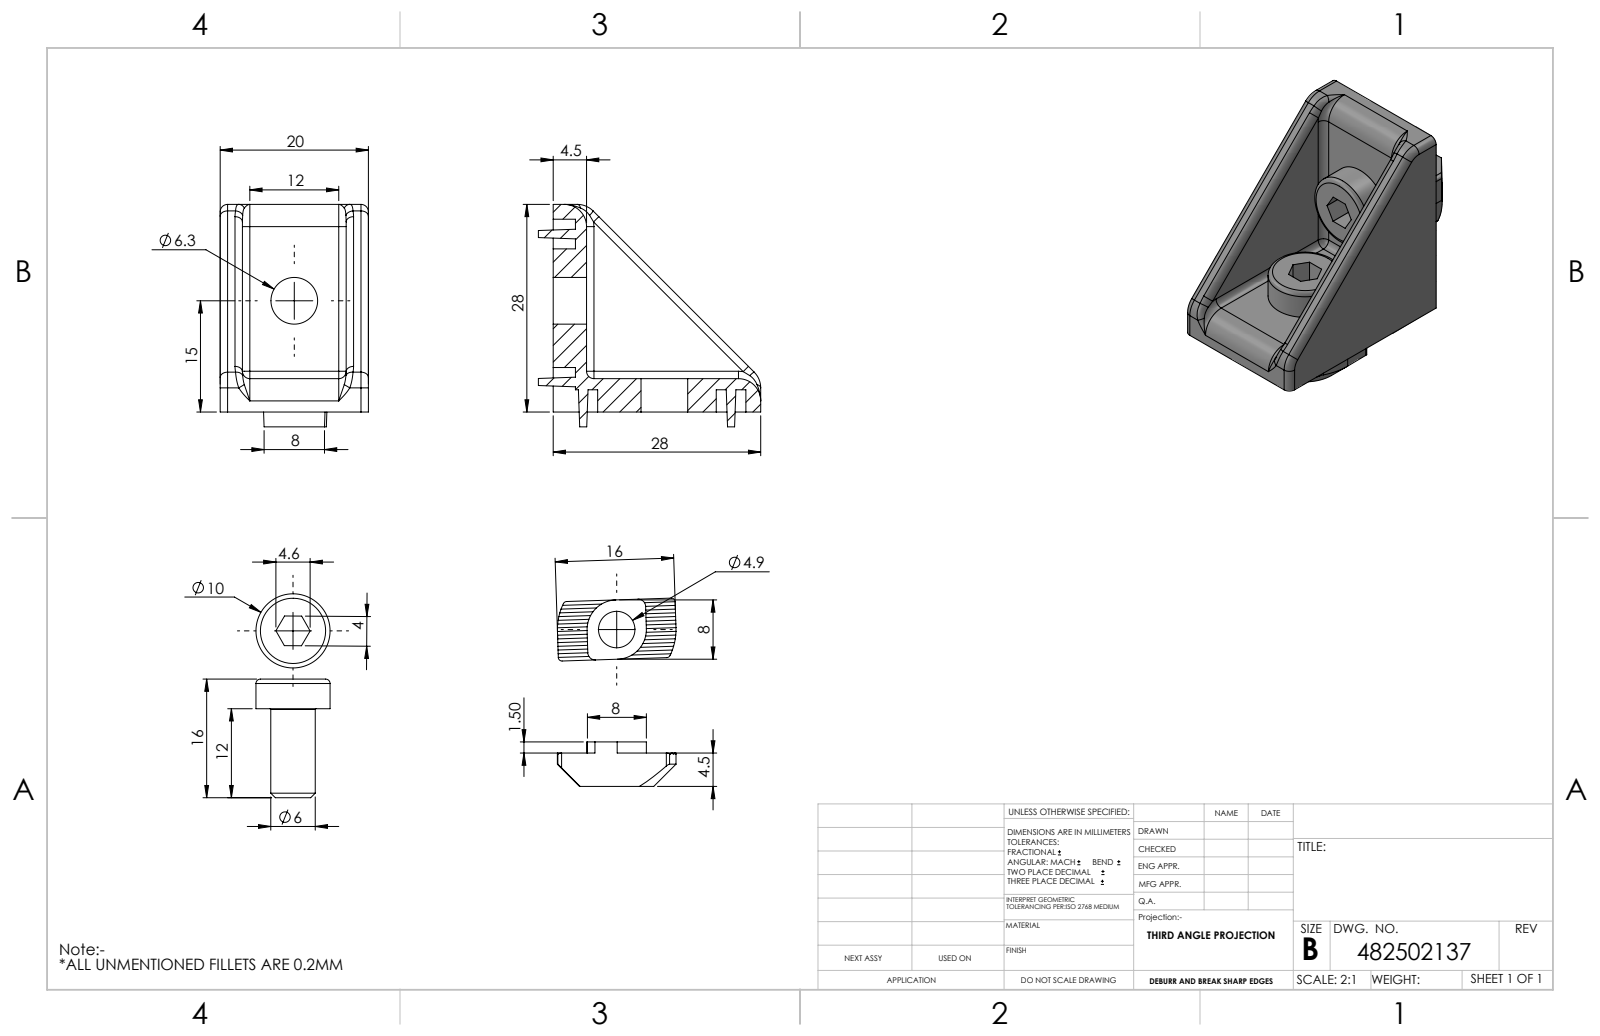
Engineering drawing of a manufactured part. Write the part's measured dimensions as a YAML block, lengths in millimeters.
part_name: "482502137 Winkel 20x28 inkl Bef; Syskomp 482501587 Winkel 20x28; DIN 7984 M6 x 12; Syskomp 482501753 Hammermutter N8 M6 verzinkt"
step_written_by: "Autodesk Inventor 2012 (AUTOMOTIVE_DESIGN)"
units: millimeters
bodies: {solids: 5, faces: 231, planar: 150, cylindrical: 47, other: 34}
overall_size: [35.5, 35.5, 20]
volume: 7630
surface_area: 6338
round_holes:
  - {diameter: 4.92, count: 2}
  - {diameter: 6.3, count: 2}
round_bosses_or_shafts:
  - {diameter: 10, count: 2}
  - {diameter: 6, count: 2}
partial_cylinders:
  - {radius: 1, count: 17}
  - {radius: 0.5, count: 8}
  - {radius: 3, count: 4}
  - {radius: 4, count: 2}
  - {radius: 8, count: 2}
face_to_face_distances: [3, 20, 4.5, 17, 4, 6, 16, 14, 1.5, 6.15]
